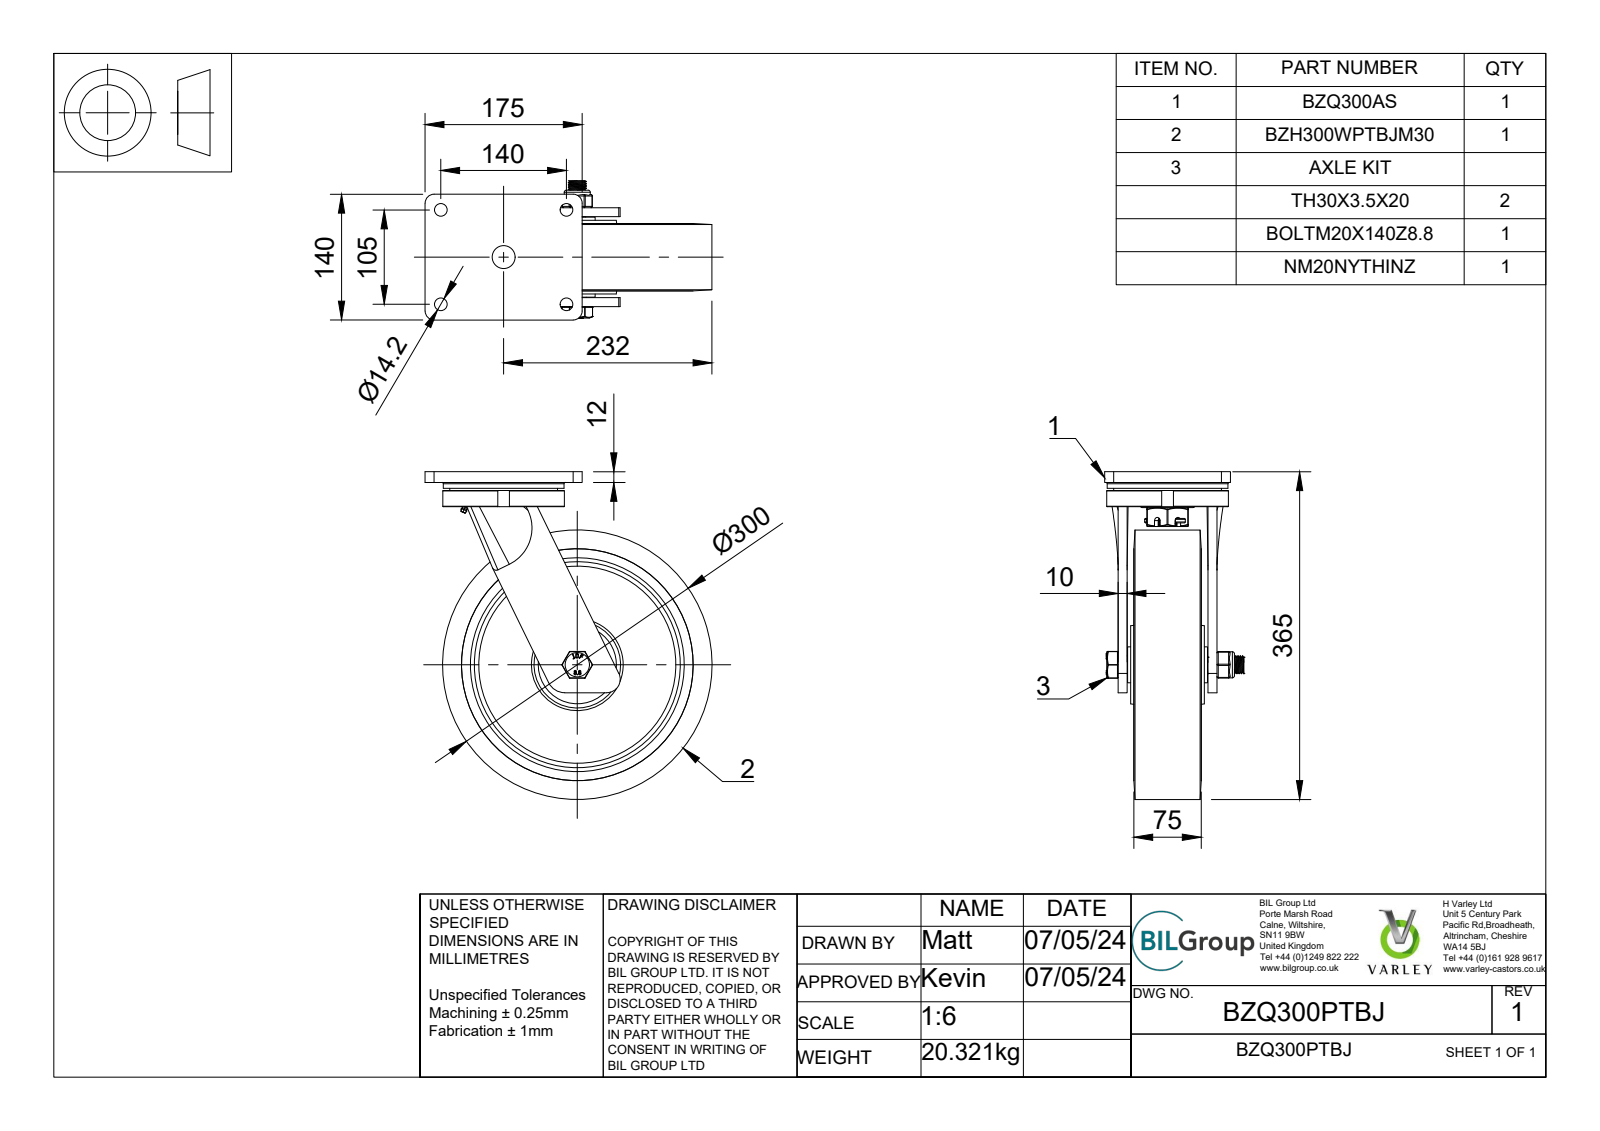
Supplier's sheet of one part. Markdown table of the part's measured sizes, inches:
| quantity | value |
| --- | --- |
| part name | BZQ300PTBJ v4; BZQ300AS v1; FABRICATED STEEL TOP PLATE; TOP PLATE (+8 more) |
| STEP written by | Autodesk Translation Framework v12.20.1.177 (AUTOMOTIVE_DESIGN) |
| units | inches |
| bodies | 40 solids, 1207 faces (397 planar, 347 cylindrical, 463 other) |
| overall size | 14.37 × 12.579 × 6.102 |
| volume | 243 in³ |
| surface area | 1 057 in² |
| round holes (diameter × count) | 0.295 × 18, 0.559 × 4, 0.276 × 2, 1.181 × 2, 0.787 × 1, 0.797 × 1, 0.807 × 1, 1.004 × 1, 1.614 × 1, 1.788 × 1, 1.85 × 1, 2.028 × 1 |
| round bosses / shafts (diameter × count) | 11.811 × 1, 5.354 × 1, 5.295 × 1, 4.724 × 1, 2.087 × 1, 1.946 × 1, 1.673 × 1, 1.594 × 1 |
| partial cylindrical surfaces (radius × count) | 0.039 × 20, 0.059 × 20, 0.226 × 18, 0.02 × 17, 0.01 × 6, 0.026 × 4, 0.05 × 4, 0.079 × 4 |
| main face-to-face distances | 0.394, 1.969, 1.575, 2.362, 3.937, 0.472, 1.28, 0.689, 1.673, 3.642 |
| hole center spacings | 2.598, 3.445, 4.134, 5.512, 6.89, 1.122, 2.335, 3.176 |
